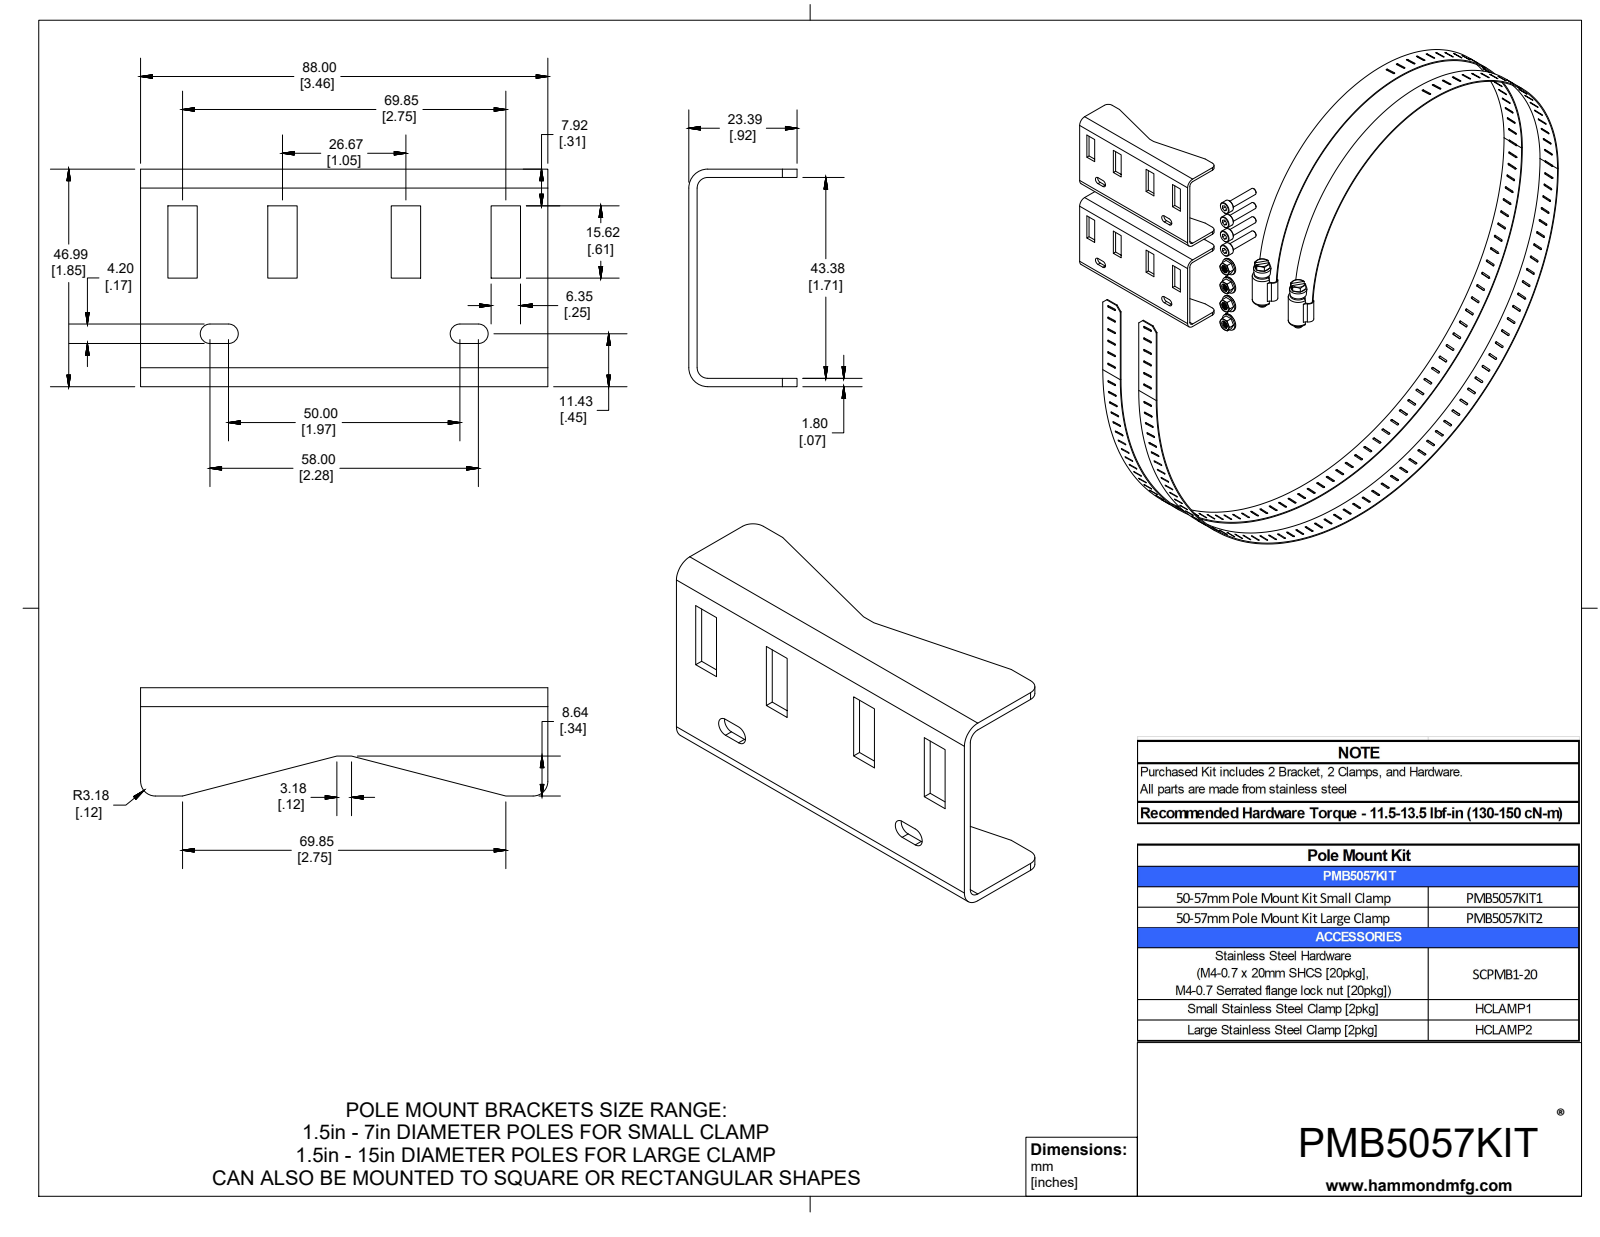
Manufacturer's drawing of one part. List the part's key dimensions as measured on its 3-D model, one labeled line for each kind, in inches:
Part name (STEP PRODUCT): PMB5057KIT1
STEP written by: SolidWorks 2019 (CONFIG_CONTROL_DESIGN)
Units: inches
Bodies: 14 solids, 1374 faces (856 planar, 448 cylindrical, 70 other)
Overall size (bounding box): 12.897 × 10.397 × 7.393
Volume: 2.625 in³ · Surface area: 136.4 in²
Round holes (diameter × count): ⌀0.13 ×4, ⌀0.166 ×4
Round bosses / shafts (diameter × count): ⌀0.394 ×4, ⌀0.293 ×4, ⌀0.272 ×4, ⌀0.157 ×4, ⌀0.313 ×2, ⌀0.22 ×2, ⌀0.2 ×2
Partial cylindrical surfaces — rounded edges, fillets, slot ends (radius × count): R0.02 ×364, R0.125 ×9, R0.098 ×8, R0.09 ×4, R0.1 ×4, R0.12 ×4, R0.161 ×4, R0.195 ×2
Main face-to-face distances: 0.071, 2.244, 1.779, 2.315, 1.708, 4.022, 0.071, 1.779, 1.85, 0.465
Hole centre spacings: 0.513, 1.027, 0.514, 1.541
